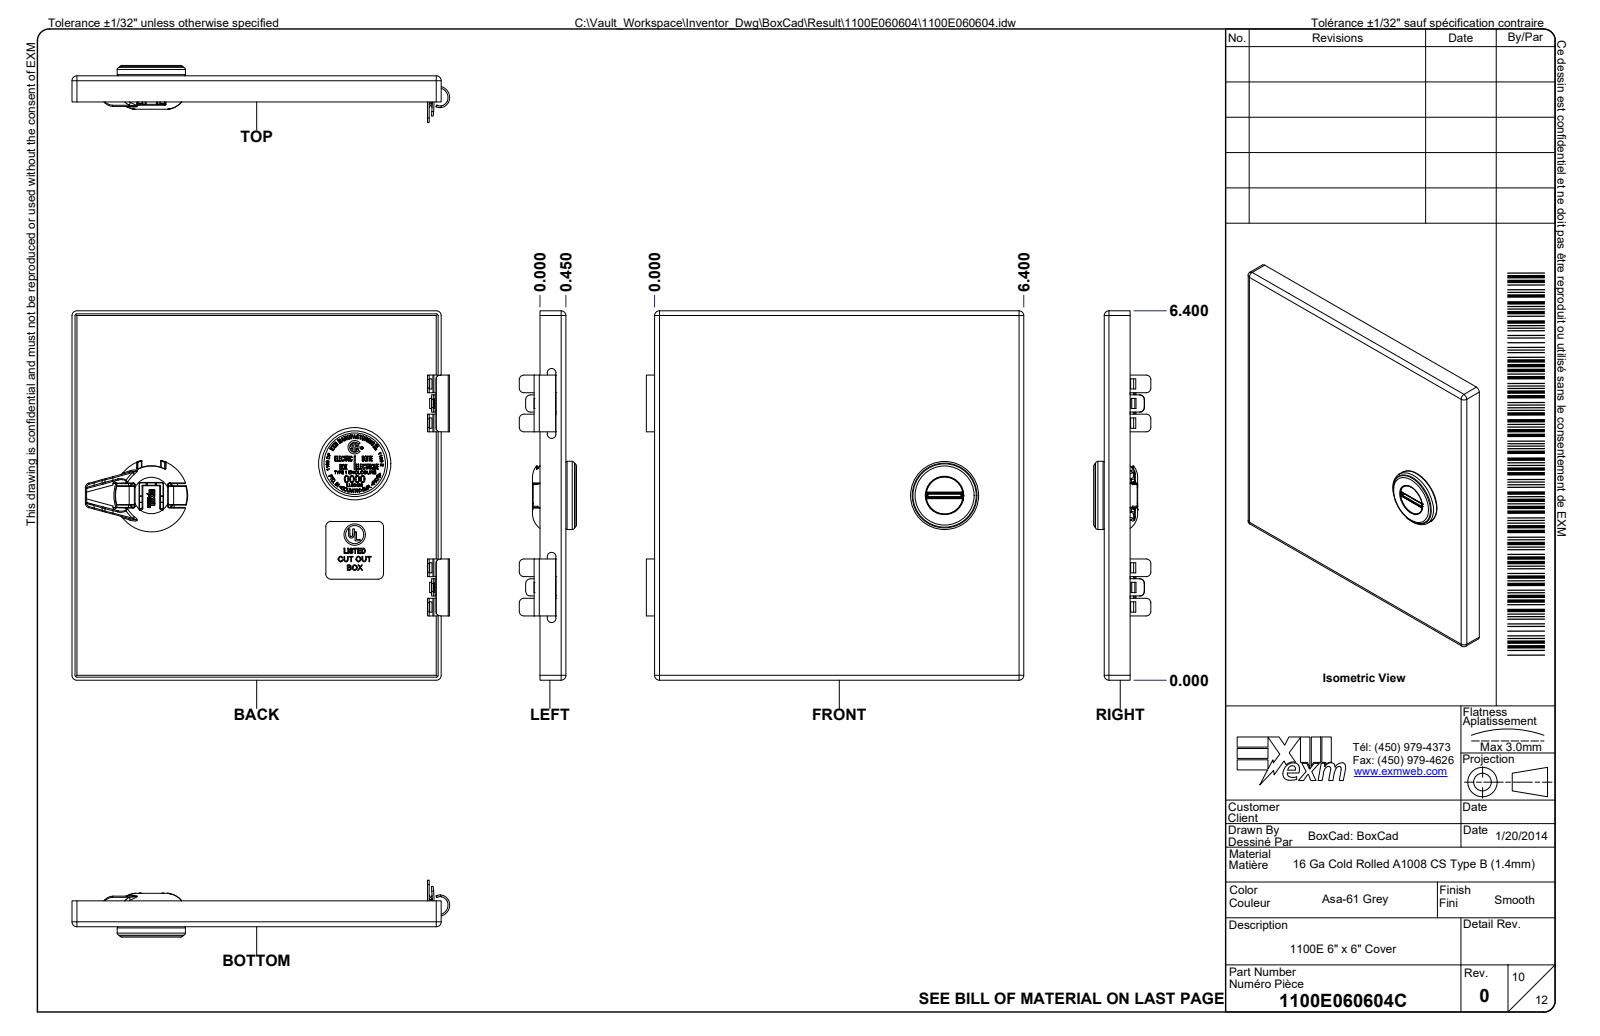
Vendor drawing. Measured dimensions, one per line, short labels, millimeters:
name: 1100E060604; 1100E060604B; 1100E060604B-P; 1100E060604C (+8 more)
written by: Autodesk Inventor 2024 (AUTOMOTIVE_DESIGN)
unit: mm
bodies: 8 solids, 3761 faces (2038 planar, 632 cylindrical, 1091 other)
size: 166.2 × 162.6 × 107.9
volume: 183 400 mm³; area: 274 600 mm²
holes: 6× ⌀28.6, 4× ⌀7.4, 4× ⌀22.2, 2× ⌀4.5, 2× ⌀34.9, 1× ⌀0.8, 1× ⌀1.1, 1× ⌀9.5, 1× ⌀27
bosses: 6× ⌀28.6, 4× ⌀22.2, 2× ⌀34.9, 1× ⌀32, 1× ⌀31.8, 1× ⌀30, 1× ⌀29, 1× ⌀20
rounds: 219× R0.3, 22× R0.8, 19× R0.5, 18× R2, 14× R2.2, 8× R2.1, 7× R0.2, 4× R1
face distances: 1.4, 151, 152.4, 149.6, 1.3, 102, 103.3, 100.6, 101.9, 100.2
hole spacings: 43, 101.6, 52.8, 76.7, 85.8, 115.1, 143.7, 7.6
